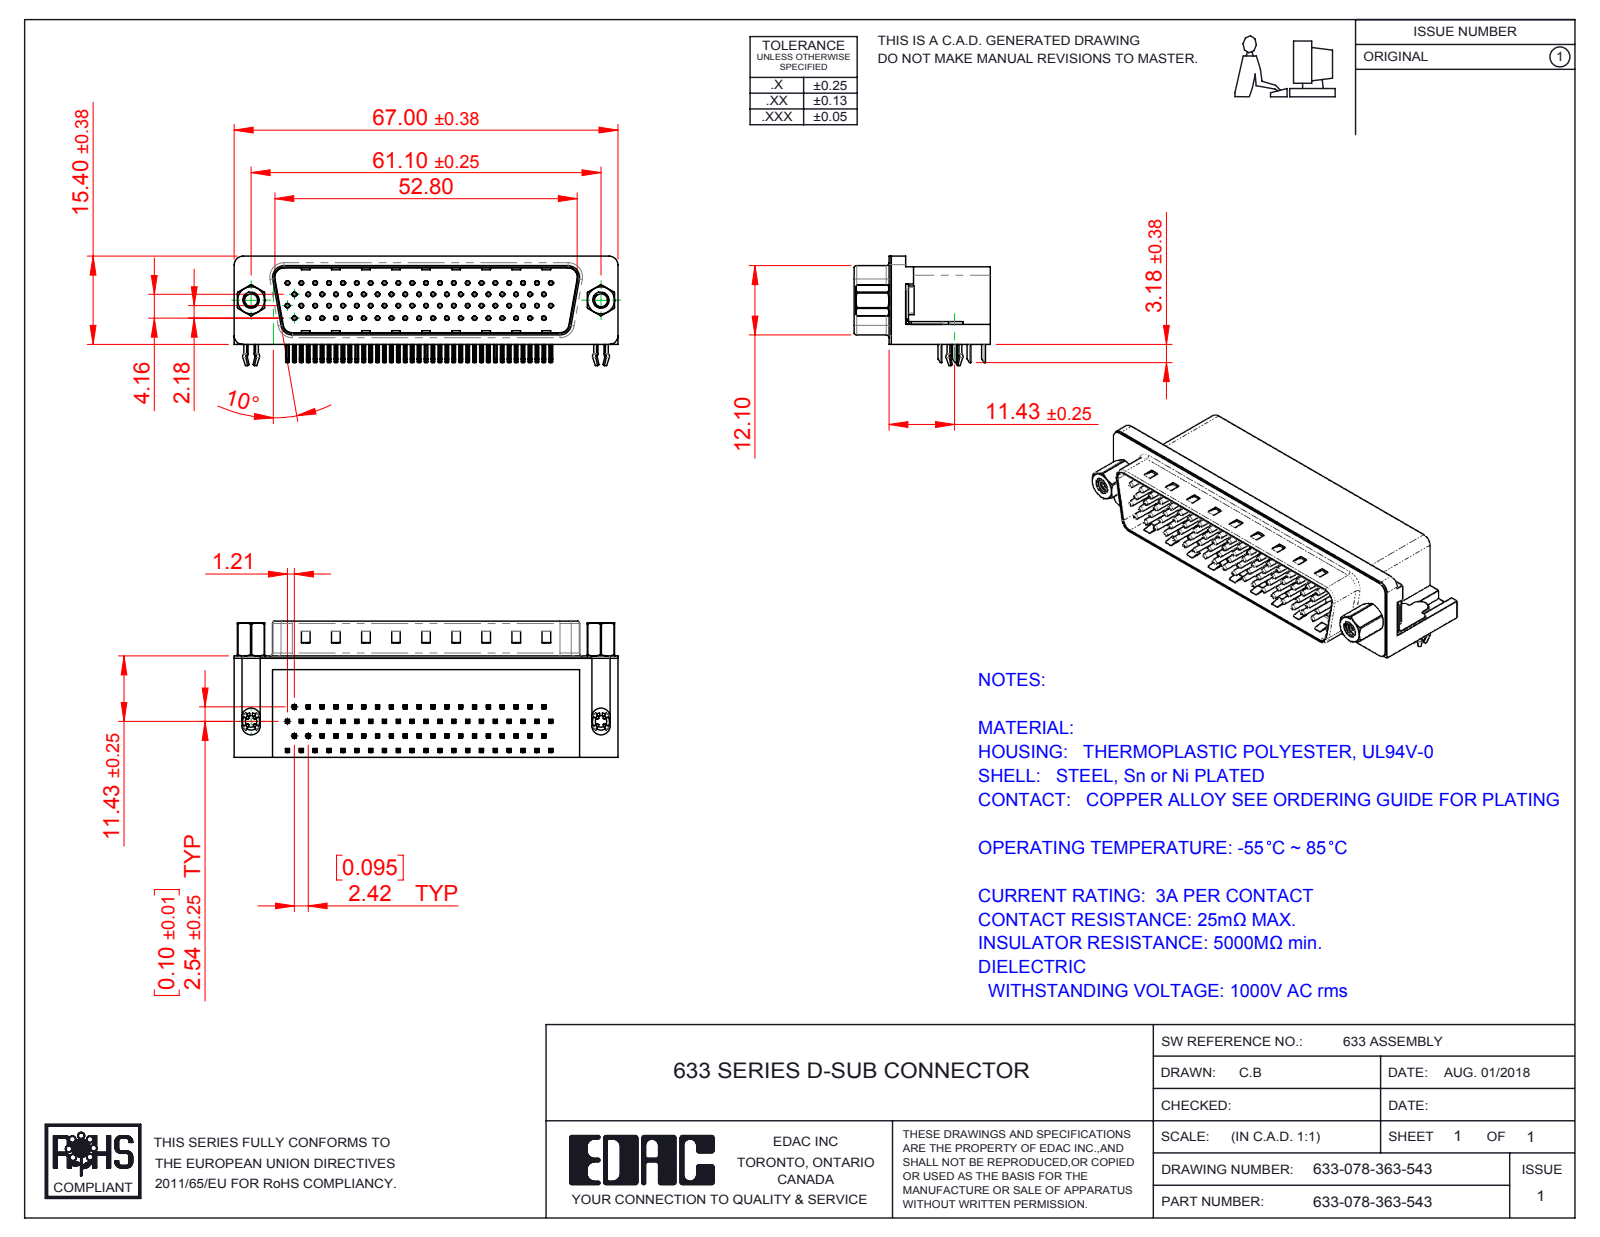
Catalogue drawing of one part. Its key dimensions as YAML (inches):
part_name: "633-078-363-543; 633 Contact Top_78 Contact; 633 Contact Top 78; 633 Shell_78 Contact (+6 more)"
step_written_by: "SolidWorks 2016 (CONFIG_CONTROL_DESIGN)"
units: inches
bodies: {solids: 86, faces: 6516, planar: 4045, cylindrical: 1848, other: 623}
overall_size: [2.638, 0.937, 0.752]
volume: 0.905
surface_area: 26.17
round_holes:
  - {diameter: 0.014, count: 78}
  - {diameter: 0.031, count: 78}
  - {diameter: 0.079, count: 2}
  - {diameter: 0.089, count: 2}
  - {diameter: 0.09, count: 2}
  - {diameter: 0.157, count: 2}
  - {diameter: 0.189, count: 2}
  - {diameter: 0.197, count: 2}
round_bosses_or_shafts:
  - {diameter: 0.03, count: 78}
  - {diameter: 0.193, count: 2}
  - {diameter: 0.187, count: 2}
  - {diameter: 0.154, count: 2}
  - {diameter: 0.118, count: 2}
  - {diameter: 0.11, count: 2}
partial_cylinders:
  - {radius: 0.01, count: 324}
  - {radius: 0.005, count: 156}
  - {radius: 0.039, count: 16}
  - {radius: 0.02, count: 9}
  - {radius: 0.063, count: 8}
  - {radius: 0.059, count: 6}
  - {radius: 0.018, count: 4}
  - {radius: 0.035, count: 4}
face_to_face_distances: [0.016, 0.52, 0.681, 0.461, 0.526, 0.081, 0.541, 0.065, 0.073, 0.469]
hole_center_spacings: [0.095, 0.191, 0.286, 0.381, 0.246, 0.281, 0.476, 0.339]
